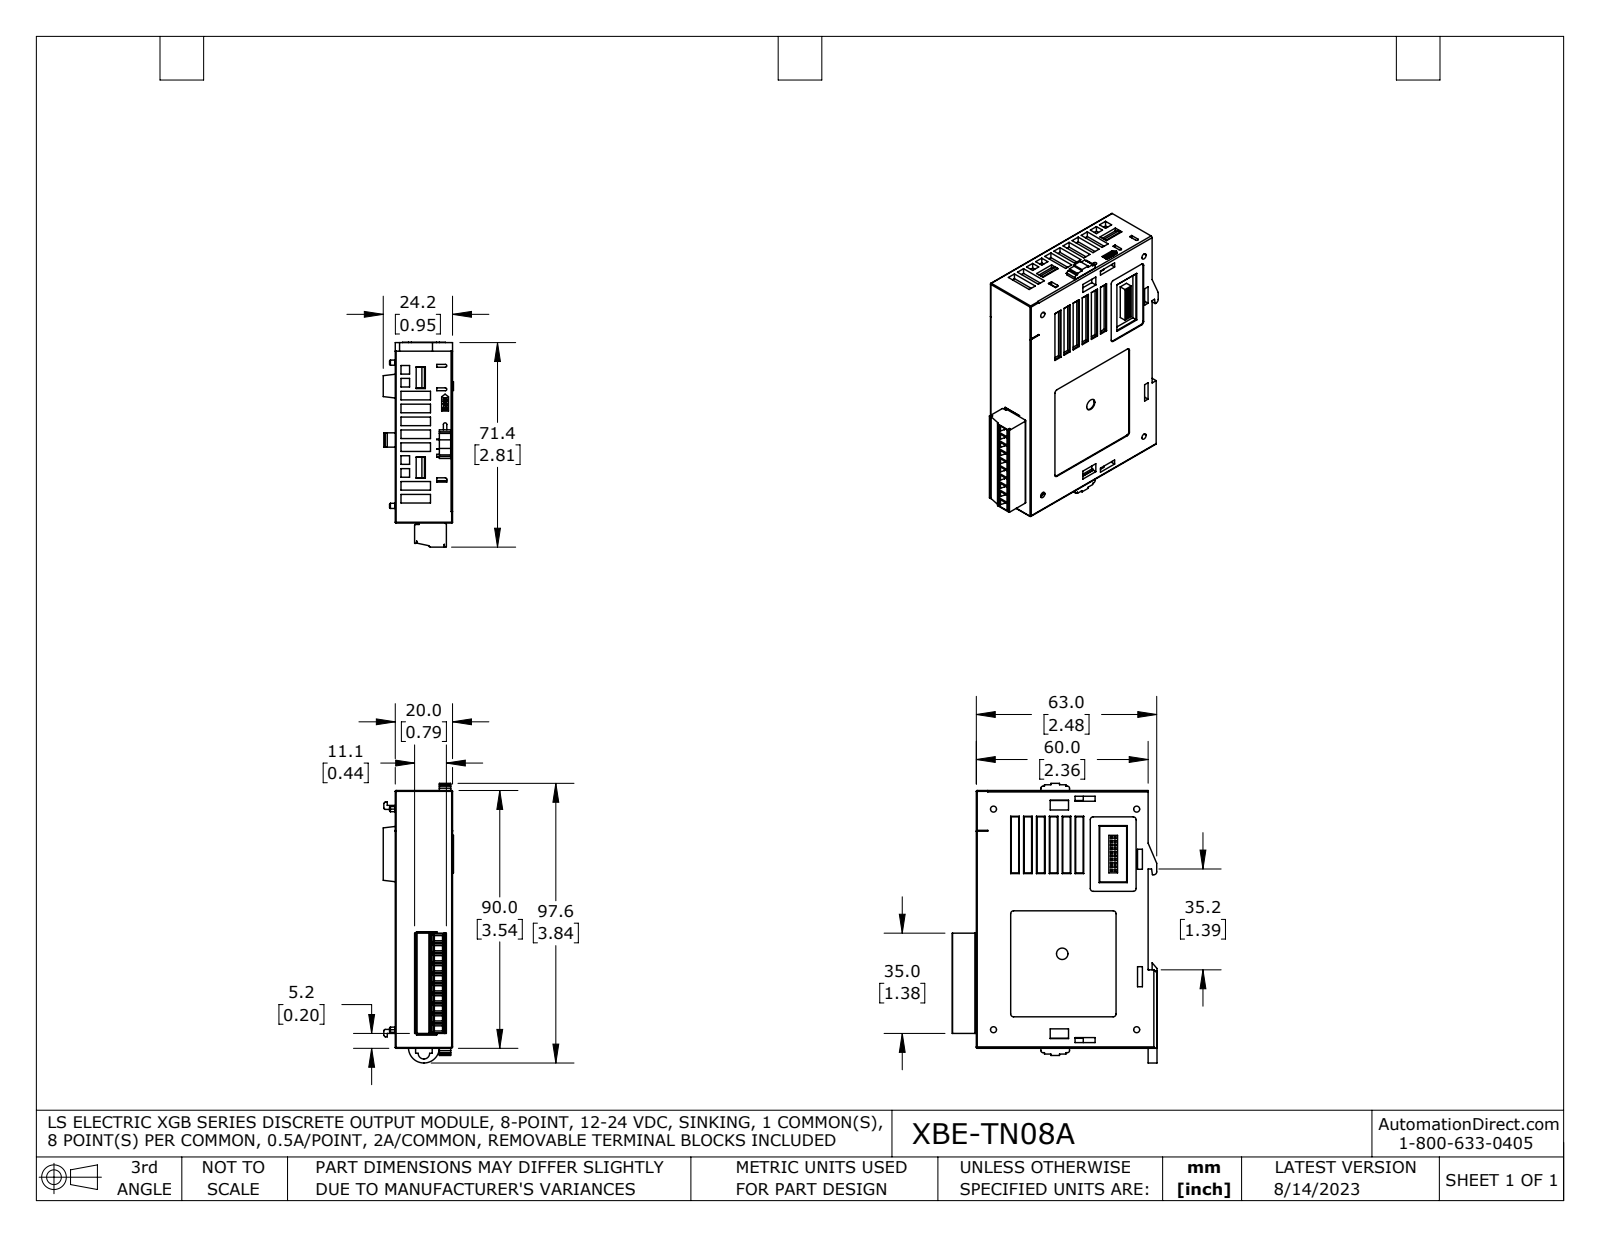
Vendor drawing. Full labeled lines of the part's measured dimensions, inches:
Part name (STEP PRODUCT): XBE-TN08A nc din clip 6 bad faces cut1 coord fxt
STEP written by: SolidWorks 2021 (AUTOMOTIVE_DESIGN)
Units: inches
Bodies: 1 solid, 2347 faces (1755 planar, 404 cylindrical, 188 other)
Overall size (bounding box): 3.844 × 2.815 × 0.966
Volume: 6.571 in³ · Surface area: 45.24 in²
Round holes (diameter × count): ⌀0.108 ×10, ⌀0.116 ×10, ⌀0.083 ×4, ⌀0.071 ×2, ⌀0.157 ×1
Round bosses / shafts (diameter × count): ⌀0.11 ×10, ⌀0.071 ×6
Partial cylindrical surfaces — rounded edges, fillets, slot ends (radius × count): R0.008 ×42, R0.004 ×40, R0.012 ×38, R0.02 ×21, R0.039 ×11, R0.062 ×10, R0.071 ×10, R0.031 ×6
Main face-to-face distances: 0.787, 0.079, 0.039, 0.776, 0.709, 2.362, 0.748, 0.669, 0.067, 0.031
Hole centre spacings: 0.138, 0.276, 0.413, 0.551, 0.689, 0.827, 0.965, 0.539
